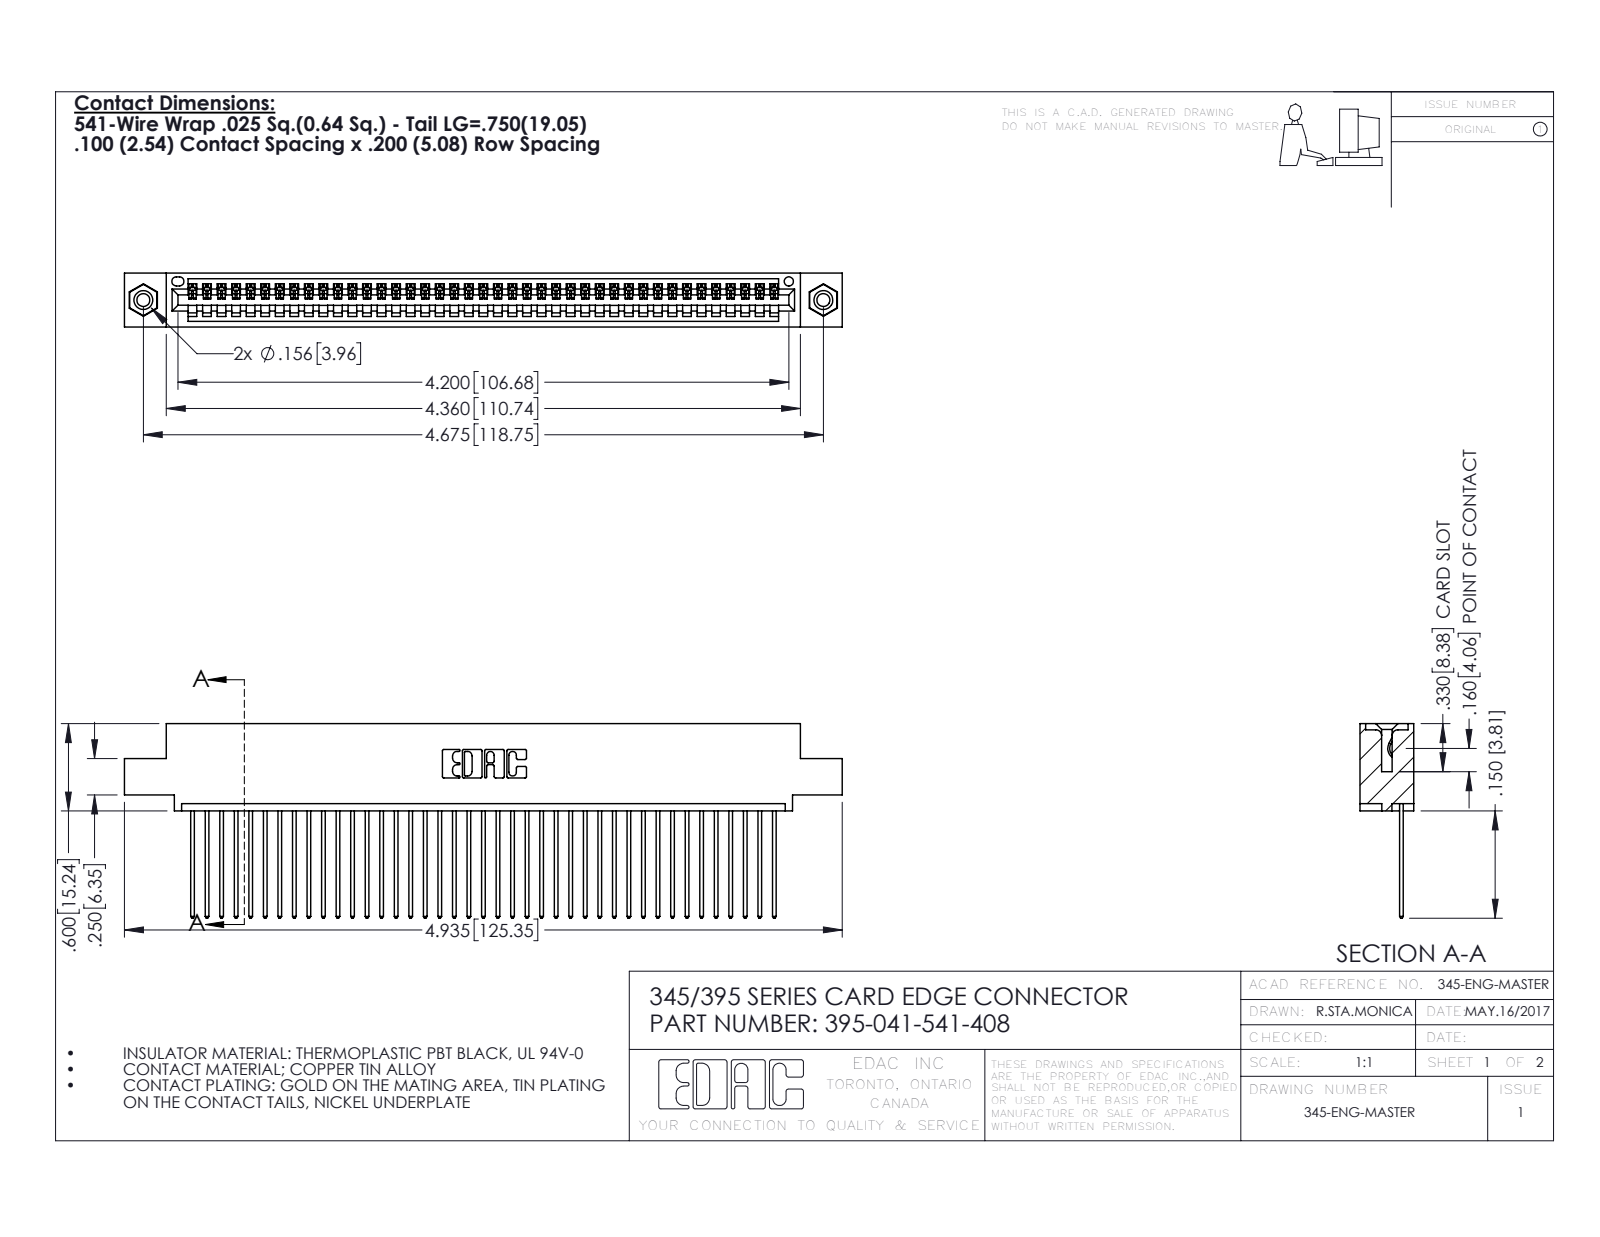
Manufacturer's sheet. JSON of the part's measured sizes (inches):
{"part_name": "345-292-001_345-293-141; 345-250-001_345-250-003-102; 345 Part_0.110 Offset - 0.156 Dia-TI; 395-041-541-408", "step_written_by": "SolidWorks 2016 (CONFIG_CONTROL_DESIGN)", "units": "inches", "bodies": {"solids": 44, "faces": 2568, "planar": 1756, "cylindrical": 796, "other": 16}, "overall_size": [4.935, 1.337, 0.37], "volume_in3": 0.729, "surface_area_in2": 25.99, "round_holes": [[0.089, 2], [0.125, 2], [0.156, 2], [0.064, 1]], "round_bosses_or_shafts": [[0.155, 2]], "partial_cylinders_radius": [[0.006, 82], [0.01, 82], [0.01, 22], [0.007, 6], [0.031, 6], [0.026, 3], [0.031, 2], [0.04, 2]], "face_to_face_distances": [0.072, 0.298, 0.098, 0.272, 0.025, 0.37, 0.2, 0.225, 0.149, 0.072], "hole_center_spacings": [0.27, 4.439, 4.675]}
